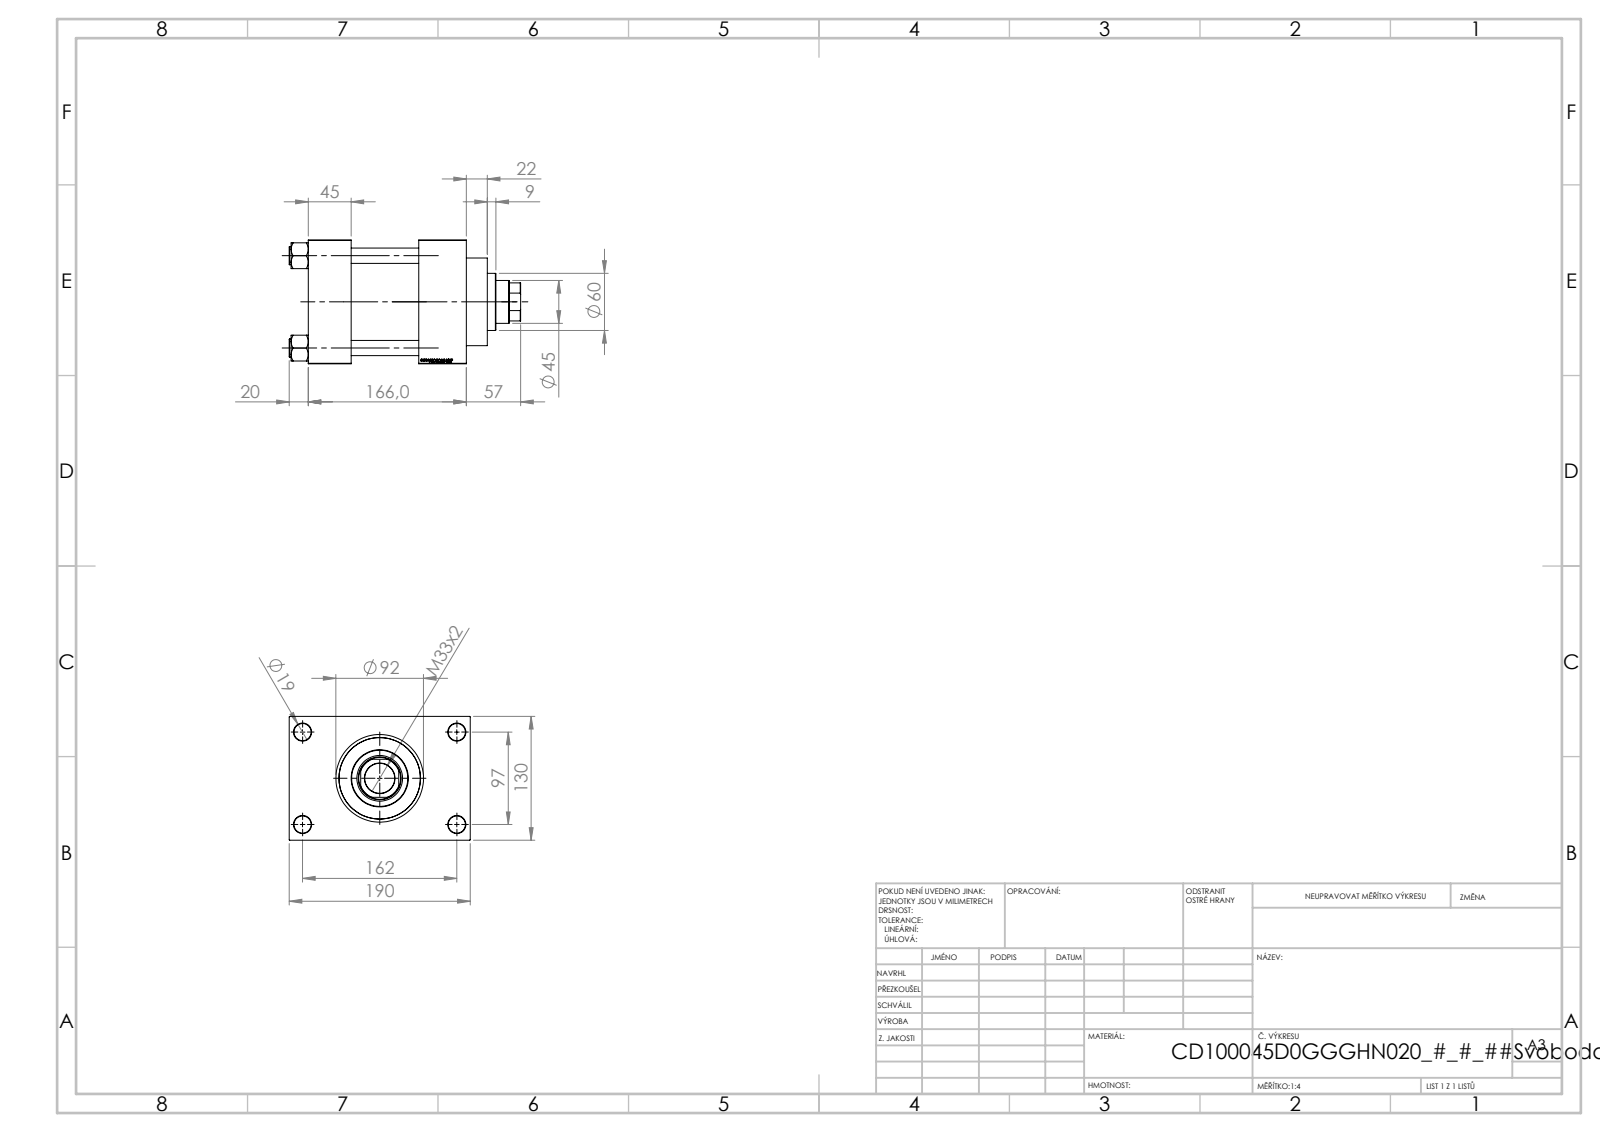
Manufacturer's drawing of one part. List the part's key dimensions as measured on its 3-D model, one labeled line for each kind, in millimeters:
Part name (STEP PRODUCT): V215CD_NUT_M5_D; V215CD_D_Body; V215CD_VC_A; V215CD_VCP_D (+1 more)
STEP written by: SolidWorks 2019 (CONFIG_CONTROL_DESIGN)
Units: millimetres
Bodies: 11 solids, 1152 faces (545 planar, 89 cylindrical, 518 other)
Overall size (bounding box): 243 × 190 × 130
Volume: 2 607 000 mm³ · Surface area: 352 394 mm²
Round holes (diameter × count): ⌀16 ×4, ⌀18 ×4, ⌀7 ×2, ⌀26.44 ×2, ⌀35 ×2, ⌀31.5 ×1, ⌀45 ×1, ⌀48 ×1, ⌀76 ×1, ⌀85.5 ×1, ⌀100 ×1
Round bosses / shafts (diameter × count): ⌀19 ×4, ⌀106 ×1, ⌀92 ×1, ⌀60 ×1
Partial cylindrical surfaces — rounded edges, fillets, slot ends (radius × count): R22 ×1
Main face-to-face distances: 130, 45, 116, 71, 166, 121, 50, 30, 160, 20
Hole centre spacings: 32.55, 68.52, 94.41, 96.9, 102.27, 129.45, 161.73, 97
